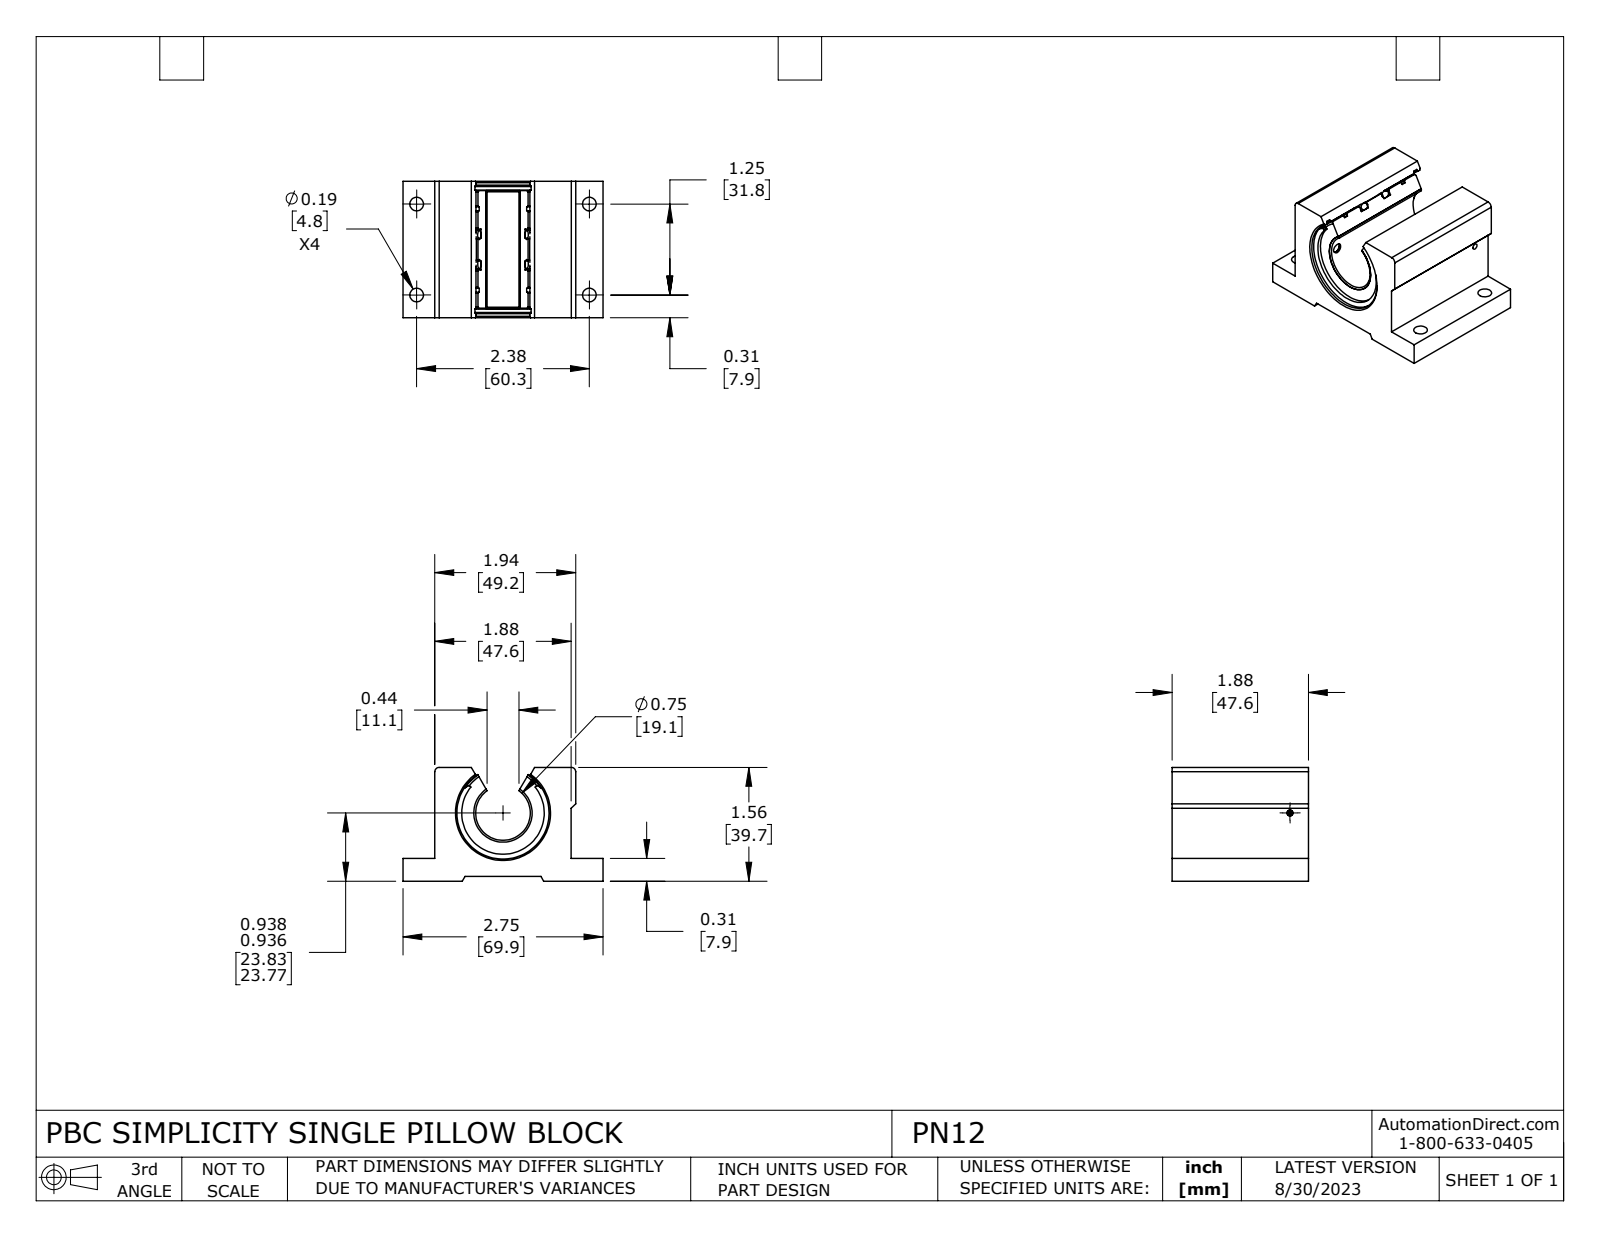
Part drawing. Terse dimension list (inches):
name: PN12
written by: SolidWorks 2021 (CONFIG_CONTROL_DESIGN)
unit: in
bodies: 8 solids, 206 faces (53 planar, 94 cylindrical, 59 other)
size: 2.75 × 1.875 × 1.563
volume: 4.501 in³; area: 47.74 in²
holes: 4× ⌀0.187, 1× ⌀0.054, 1× ⌀0.079, 1× ⌀0.136, 1× ⌀0.751, 1× ⌀0.802, 1× ⌀1.267, 1× ⌀1.33
bosses: 1× ⌀1.249, 1× ⌀1.177, 1× ⌀1.087, 1× ⌀0.078
rounds: 2× R0.03, 2× R0.06, 2× R0.18, 1× R0.567, 1× R0.676
face distances: 1.875, 0.065, 1.563, 1.498, 0.312, 0.247, 1.251, 0.437, 2.312, 0.129
hole spacings: 1.25, 2.375, 2.684, 1.368
